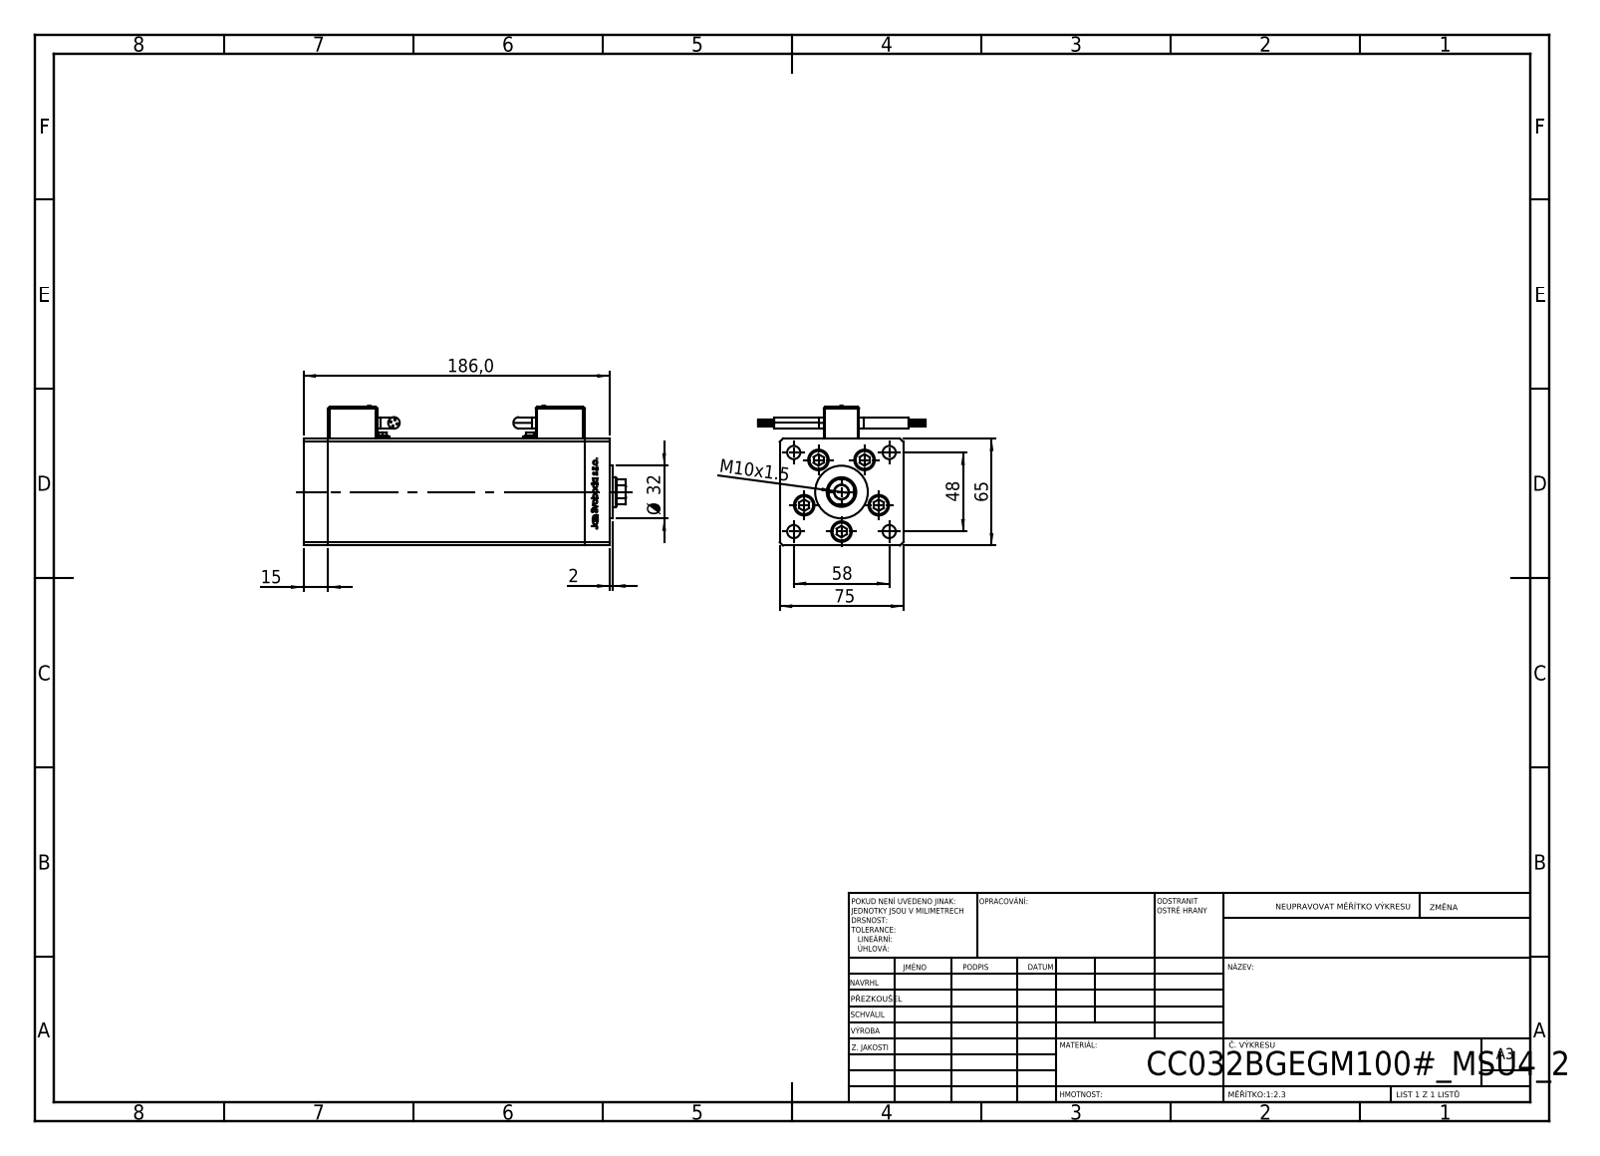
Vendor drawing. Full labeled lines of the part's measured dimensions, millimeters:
Part name (STEP PRODUCT): V220C BACK_B; V220C_FRONT_B; Magnetic_Switch_MSU4; V220C_VC_B (+2 more)
STEP written by: SolidWorks 2019 (CONFIG_CONTROL_DESIGN)
Units: millimetres
Bodies: 16 solids, 1387 faces (540 planar, 237 cylindrical, 610 other)
Overall size (bounding box): 196 × 101.6 × 85.1
Volume: 842 656 mm³ · Surface area: 147 824 mm²
Round holes (diameter × count): ⌀9 ×5, ⌀12.5 ×5, ⌀8 ×4, ⌀2 ×2, ⌀3.6 ×2, ⌀5 ×2, ⌀7 ×2, ⌀13.16 ×2, ⌀8.5 ×1, ⌀18 ×1
Round bosses / shafts (diameter × count): ⌀0.85 ×8, ⌀8 ×5, ⌀7 ×4, ⌀6 ×2, ⌀3.5 ×2, ⌀2.5 ×2, ⌀32 ×1
Partial cylindrical surfaces — rounded edges, fillets, slot ends (radius × count): R1 ×24, R4 ×4, R0.93 ×2, R8.5 ×1
Main face-to-face distances: 75, 65, 15, 156, 171, 186, 58.5, 6.5, 48.3, 26.7
Hole centre spacings: 24, 37.64, 8.25, 15.67, 17.22, 21.26, 27.71, 28
